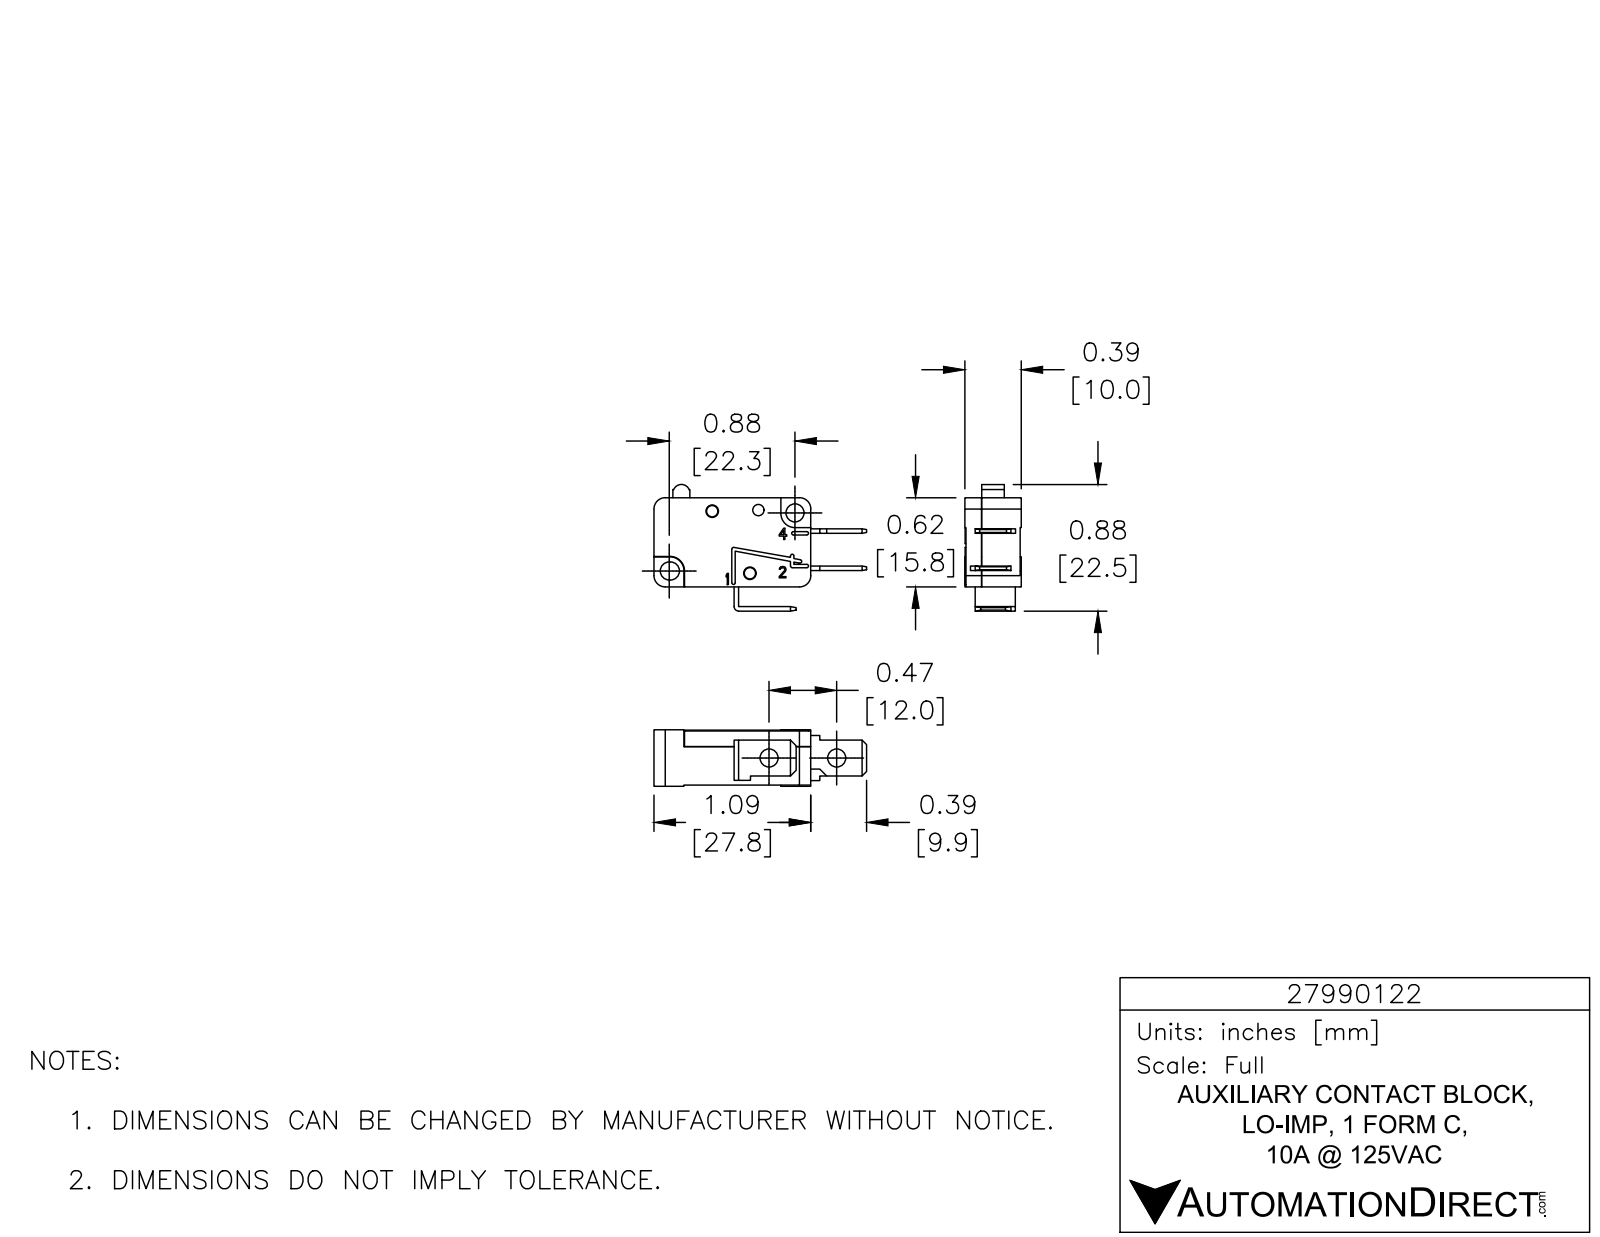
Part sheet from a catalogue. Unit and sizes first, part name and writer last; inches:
Units: inches
Overall size (bounding box): 1.484 × 0.884 × 0.394
Round holes (diameter × count): ⌀0.126 ×3, ⌀0.087 ×2, ⌀0.035 ×1, ⌀0.079 ×1
Round bosses / shafts (diameter × count): ⌀0.079 ×2, ⌀0.069 ×1
Partial cylindrical surfaces — rounded edges, fillets, slot ends (radius × count): R0.012 ×9, R0.021 ×5, R0.079 ×4, R0.017 ×3, R0.008 ×2, R0.009 ×2, R0.01 ×2, R0.025 ×2
Main face-to-face distances: 0.268, 0.27, 0.378, 0.11, 0.108, 0.622, 0.031, 1.094, 0.26, 0.543
Hole centre spacings: 0.257, 0.29, 0.323, 0.445, 0.472, 0.507, 0.526, 0.579
Volume: 0.252 in³ · Surface area: 5.198 in²
Bodies: 3 solids, 337 faces (238 planar, 97 cylindrical, 2 other)
Part name (STEP PRODUCT): 27990122
STEP written by: SolidWorks 2015 (AUTOMOTIVE_DESIGN)
